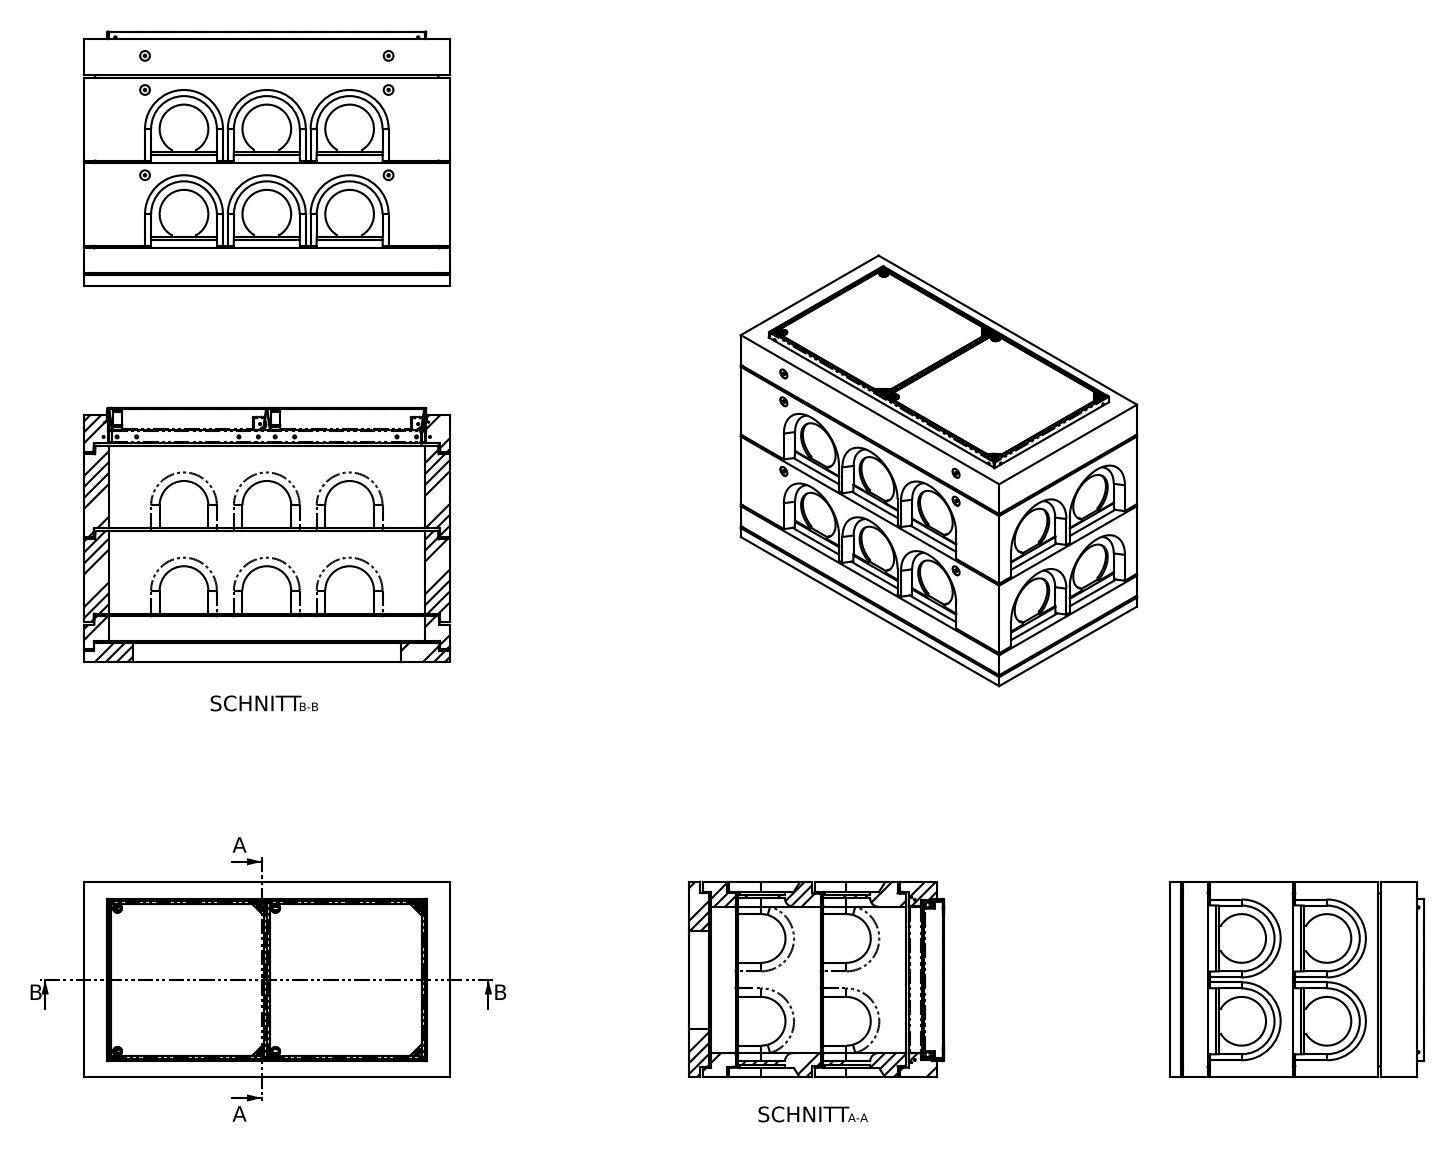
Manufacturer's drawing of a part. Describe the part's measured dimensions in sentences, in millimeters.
The part is named "SC-ECO.0613.98.125". Its 3-D file was written by "SolidWorks 2018 (AUTOMOTIVE_DESIGN)". It is 0 solids with 494 faces: 313 planar, 108 cylindrical and 73 other. Overall it measures 1500 by 1045 by 800 millimeters. Round holes: 10 of diameter 200, 4 of diameter 10, 4 of diameter 26.5, 4 of diameter 35, 4 of diameter 40. Round bosses or shafts: 6 of diameter 5.81, 2 of diameter 10. Partial cylindrical surfaces (rounded edges, fillets, slot ends): 20 of radius 35, 8 of radius 3, 6 of radius 2.5, 4 of radius 13.5. The main face-to-face distances are 100, 10, 50, 700, 800, 35, 25, 350, 1044, 315. The hole center spacings are 350, 340, 487.95, 226.27, 524.98, 855.1, 246.96, 248.39.
